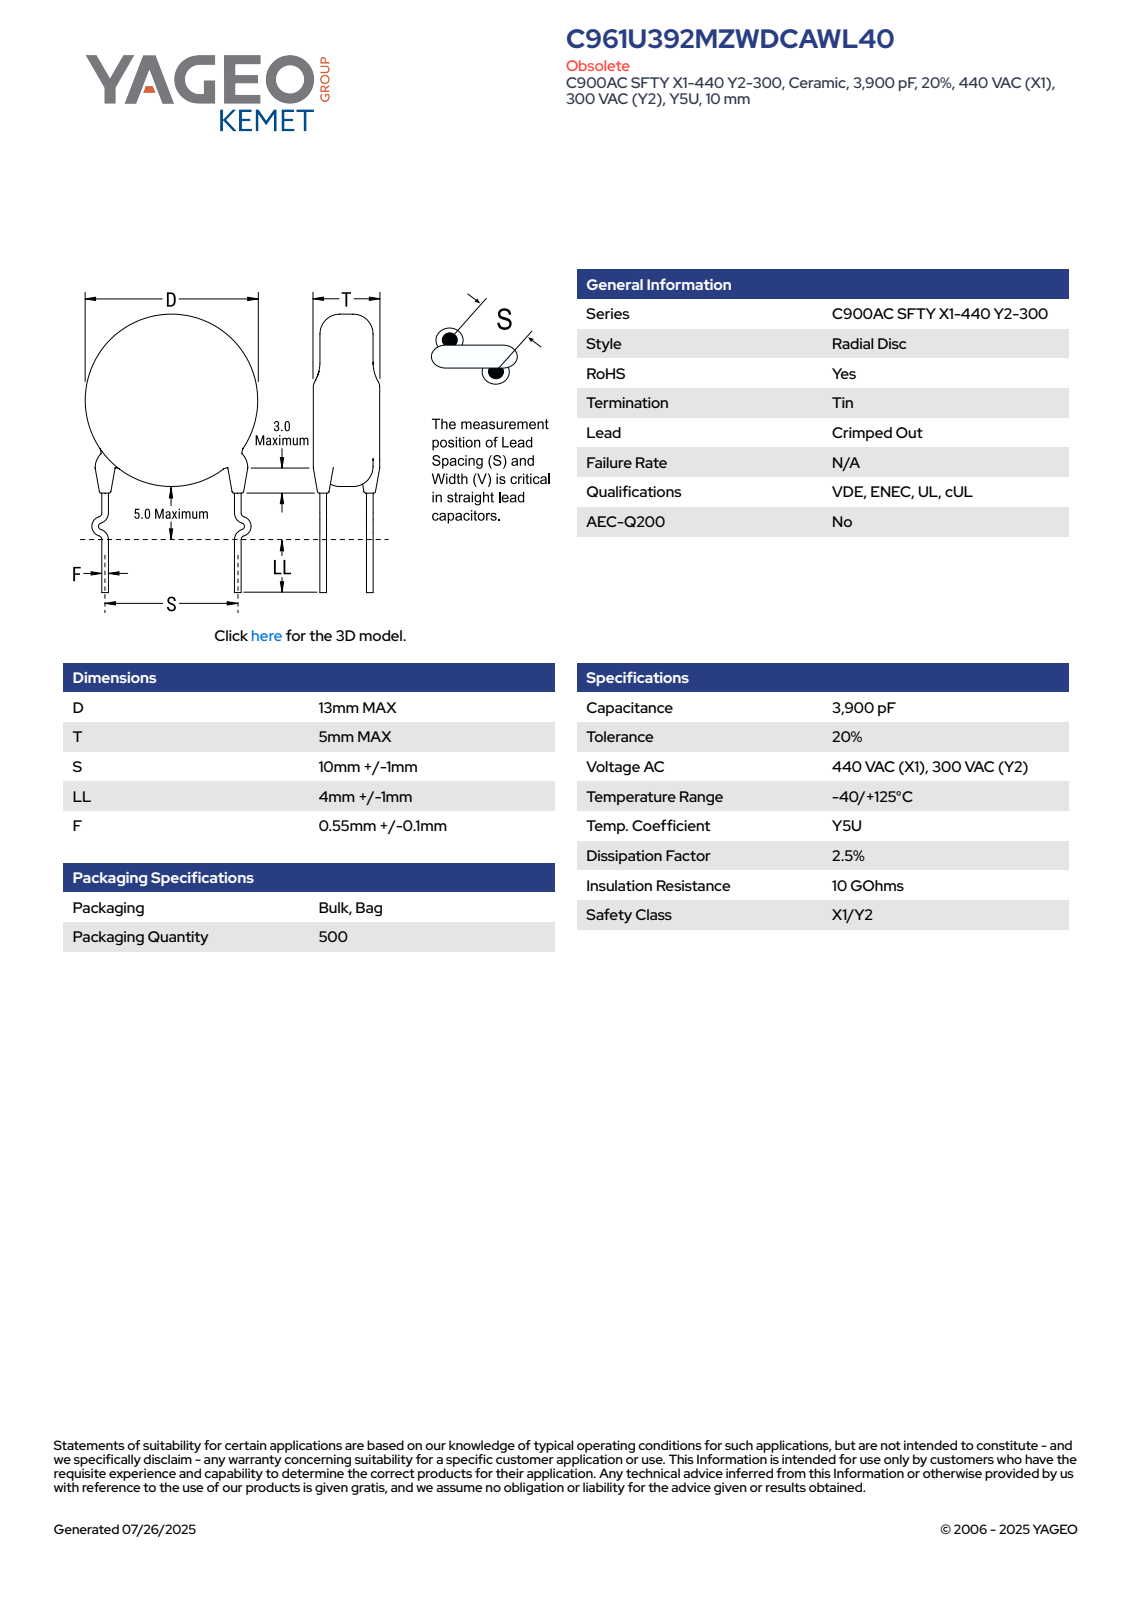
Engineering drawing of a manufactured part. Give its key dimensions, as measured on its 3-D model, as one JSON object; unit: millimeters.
{"part_name": "CCD_KCOC900_D13T5S10LL5F0.55", "step_written_by": "SolidWorks 2014 (AUTOMOTIVE_DESIGN)", "units": "millimeters", "bodies": {"solids": 4, "faces": 85, "planar": 63, "cylindrical": 6, "other": 16}, "overall_size": [23, 15.07, 5], "volume_mm3": 660, "surface_area_mm2": 512, "round_bosses_or_shafts": [[1.2, 2], [13, 1]], "face_to_face_distances": [5, 7.19, 5.84, 1.35, 0.37, 0.33, 1.09, 5.52, 2.79, 4.01]}
